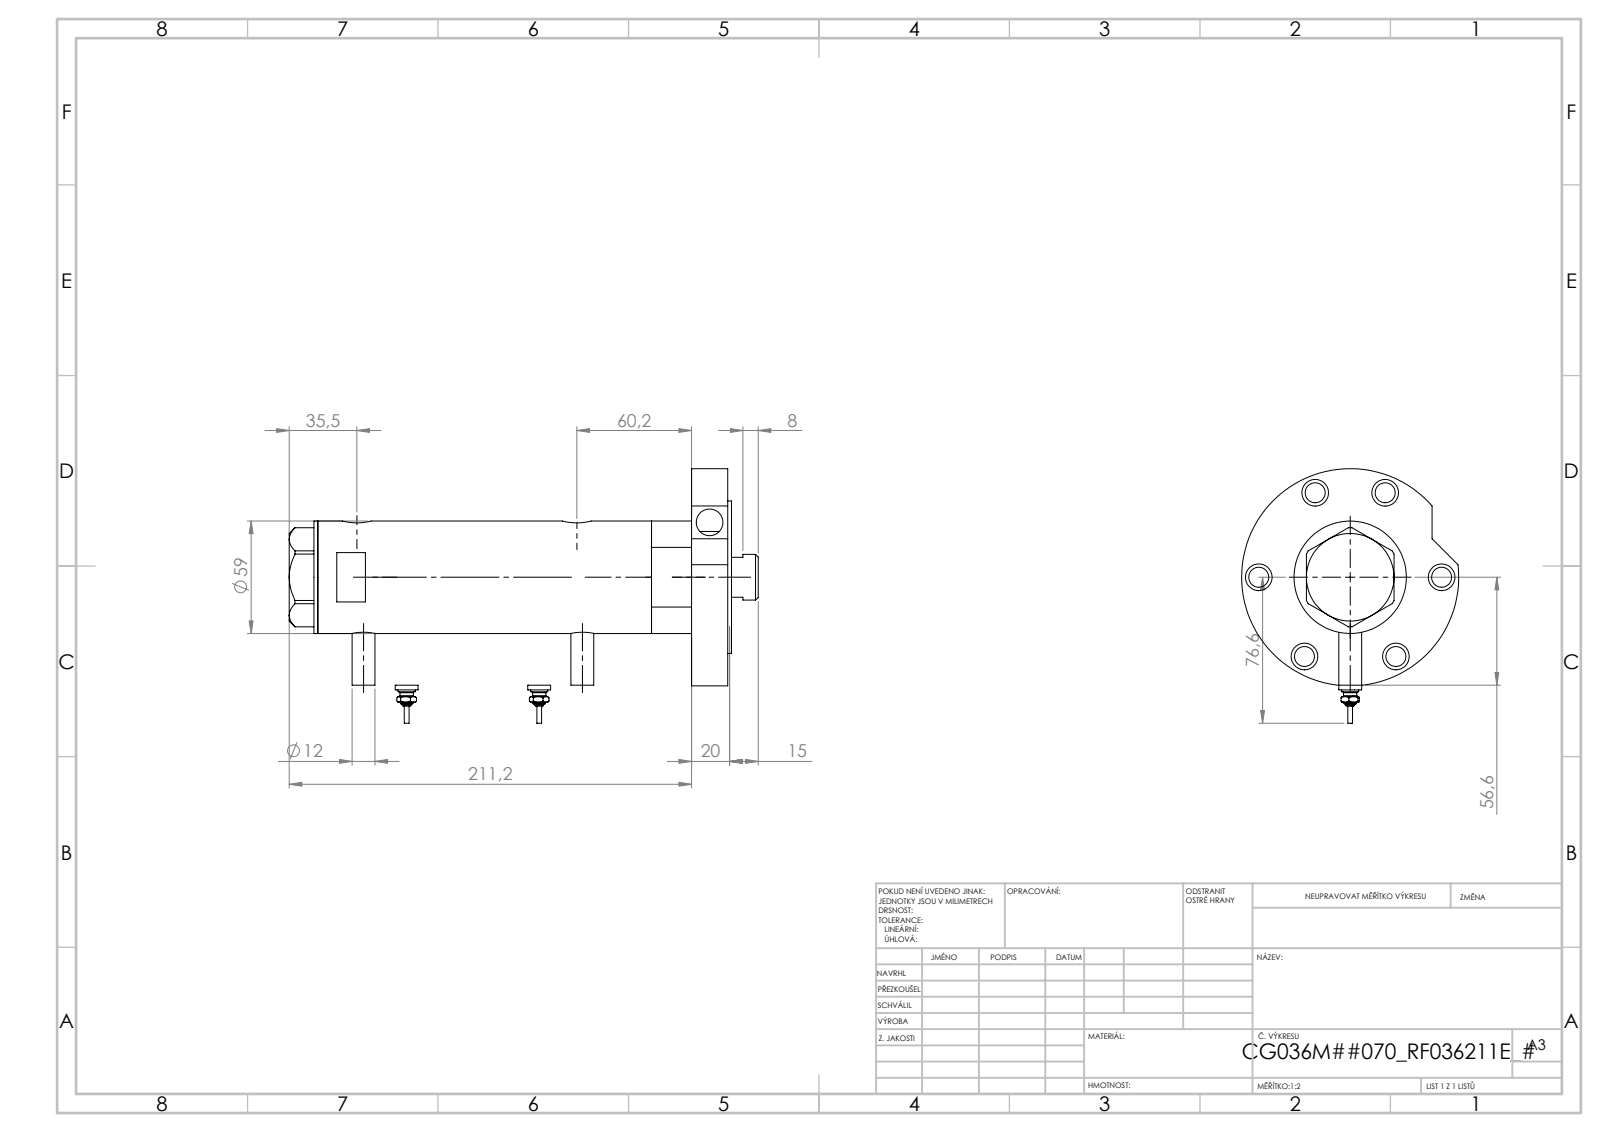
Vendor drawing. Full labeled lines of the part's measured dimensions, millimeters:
Part name (STEP PRODUCT): V270CG_VC; V270CG_RF211E; V270CG_MIDDLE; V270CG_FRONT (+2 more)
STEP written by: SolidWorks 2019 (CONFIG_CONTROL_DESIGN)
Units: millimetres
Bodies: 7 solids, 276 faces (92 planar, 110 cylindrical, 74 other)
Overall size (bounding box): 233.42 × 118.8 × 114
Volume: 664 668 mm³ · Surface area: 143 701 mm²
Round holes (diameter × count): ⌀14 ×7, ⌀10.5 ×6, ⌀5 ×2, ⌀9.73 ×2, ⌀12.5 ×2, ⌀15 ×2, ⌀8.5 ×1, ⌀25 ×1, ⌀26.5 ×1, ⌀36 ×1, ⌀40 ×1, ⌀48 ×1
Round bosses / shafts (diameter × count): ⌀12 ×4, ⌀9 ×2, ⌀7 ×2, ⌀4.34 ×2, ⌀2.4 ×2, ⌀114 ×1, ⌀80 ×1, ⌀59 ×1
Main face-to-face distances: 19, 2, 201.84, 21, 180.84, 199.84, 127.34, 53.5, 72.5, 74.5
Hole centre spacings: 48, 2.9, 3.5, 53.34, 79.82, 83.14, 86.1, 95.8
